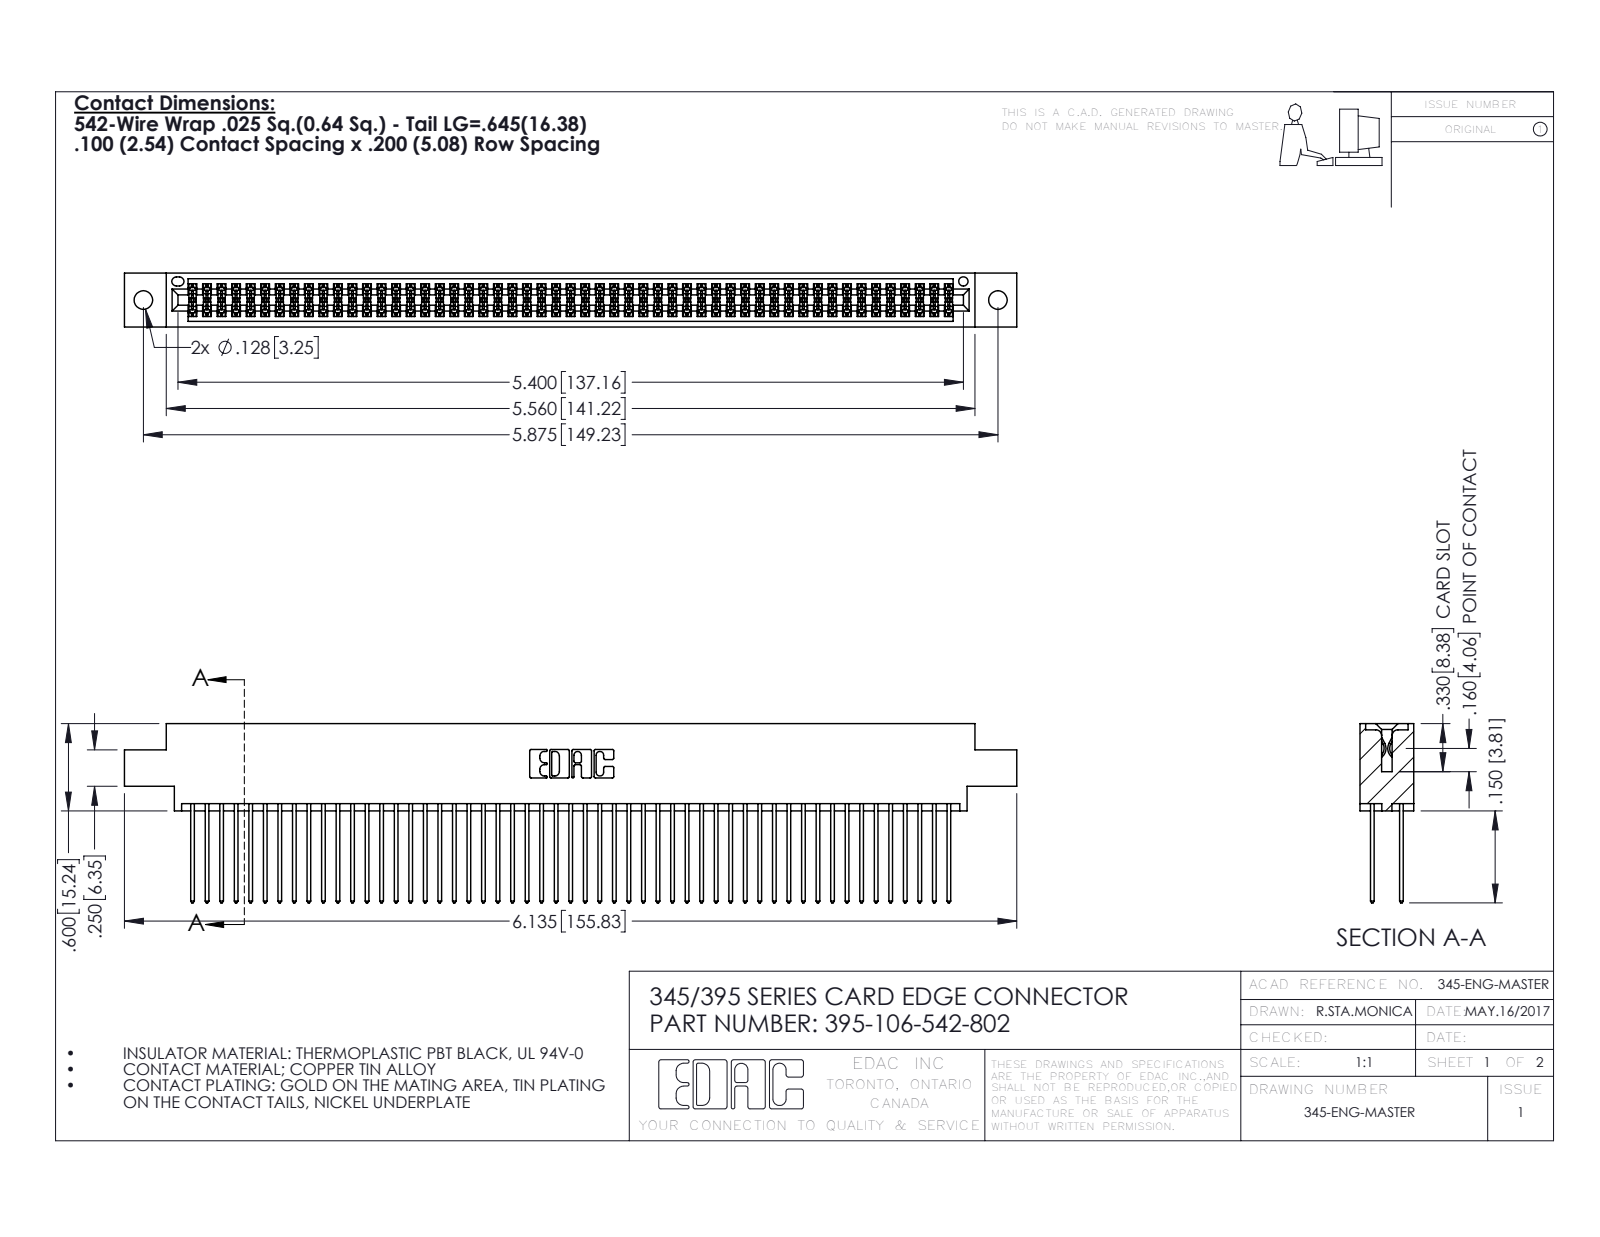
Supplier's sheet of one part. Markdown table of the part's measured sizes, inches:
| quantity | value |
| --- | --- |
| part name | 345-292-001_345-293-142; 395-106-542-802; 345 Part_0.170 Offset - 0.128 Dia |
| STEP written by | SolidWorks 2016 (CONFIG_CONTROL_DESIGN) |
| units | inches |
| bodies | 107 solids, 5430 faces (3582 planar, 1848 cylindrical, 0 other) |
| overall size | 6.135 × 1.232 × 0.37 |
| volume | 0.951 in³ |
| surface area | 39.41 in² |
| round holes (diameter × count) | 0.128 × 2, 0.064 × 1 |
| partial cylindrical surfaces (radius × count) | 0.006 × 159, 0.01 × 106, 0.01 × 22, 0.007 × 6, 0.031 × 6, 0.026 × 3, 0.014 × 2, 0.019 × 2 |
| main face-to-face distances | 0.298, 0.072, 0.2, 0.098, 0.272, 0.025, 0.37, 0.225, 0.175, 0.149 |
| hole center spacings | 0.27, 5.639, 5.875 |
